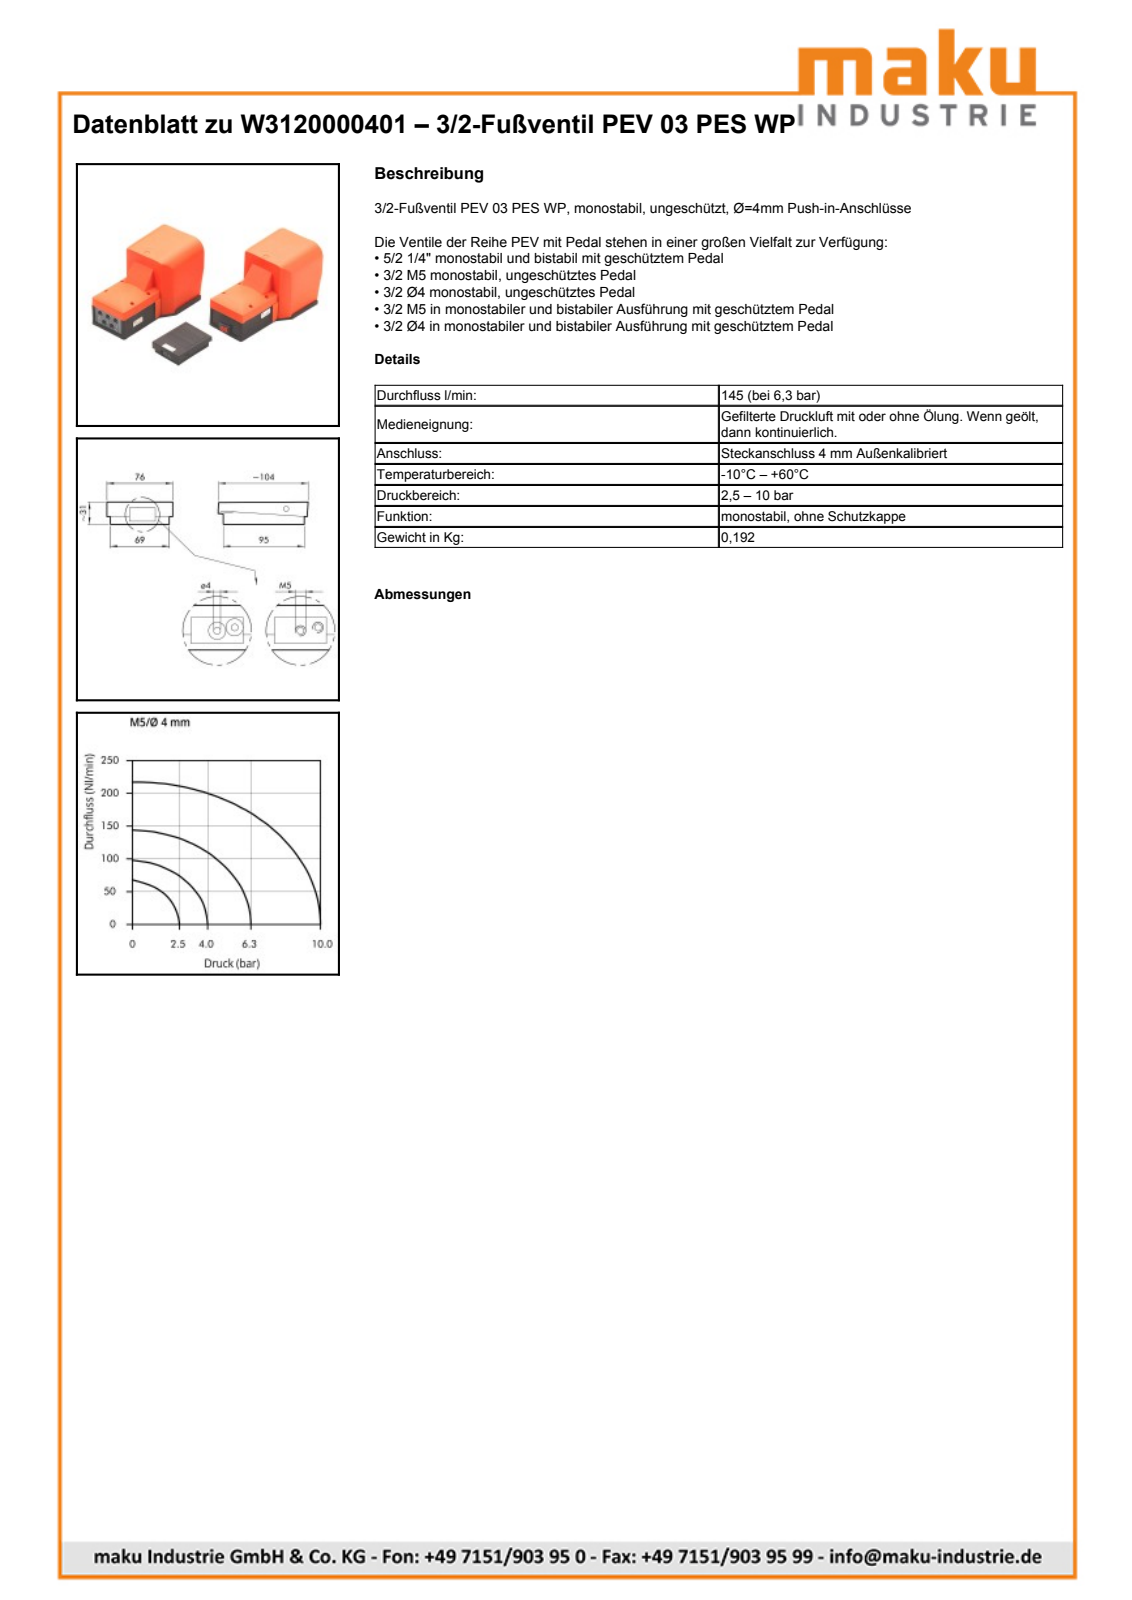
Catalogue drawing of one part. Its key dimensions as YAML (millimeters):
part_name: "W3120000401(FSWP); W3120000401Pedal; W3120000401Body; W3120000401Body1"
step_written_by: "PARTsolutions (AUTOMOTIVE_DESIGN)"
units: millimeters
bodies: {solids: 3, faces: 223, planar: 137, cylindrical: 83, other: 3}
overall_size: [104, 77, 31]
volume: 83222
surface_area: 59553
round_holes:
  - {diameter: 2.4, count: 2}
  - {diameter: 4, count: 2}
  - {diameter: 4.5, count: 2}
  - {diameter: 6, count: 1}
round_bosses_or_shafts:
  - {diameter: 10, count: 2}
  - {diameter: 6, count: 2}
  - {diameter: 4.2, count: 1}
partial_cylinders:
  - {radius: 1, count: 30}
  - {radius: 2, count: 6}
  - {radius: 4.28, count: 1}
face_to_face_distances: [2.5, 27.8, 19.5, 17, 3.5, 2, 25.8, 70, 6, 30.3]
hole_center_spacings: [9.34, 4.75, 10.41, 10.8, 18.68, 19.2]
